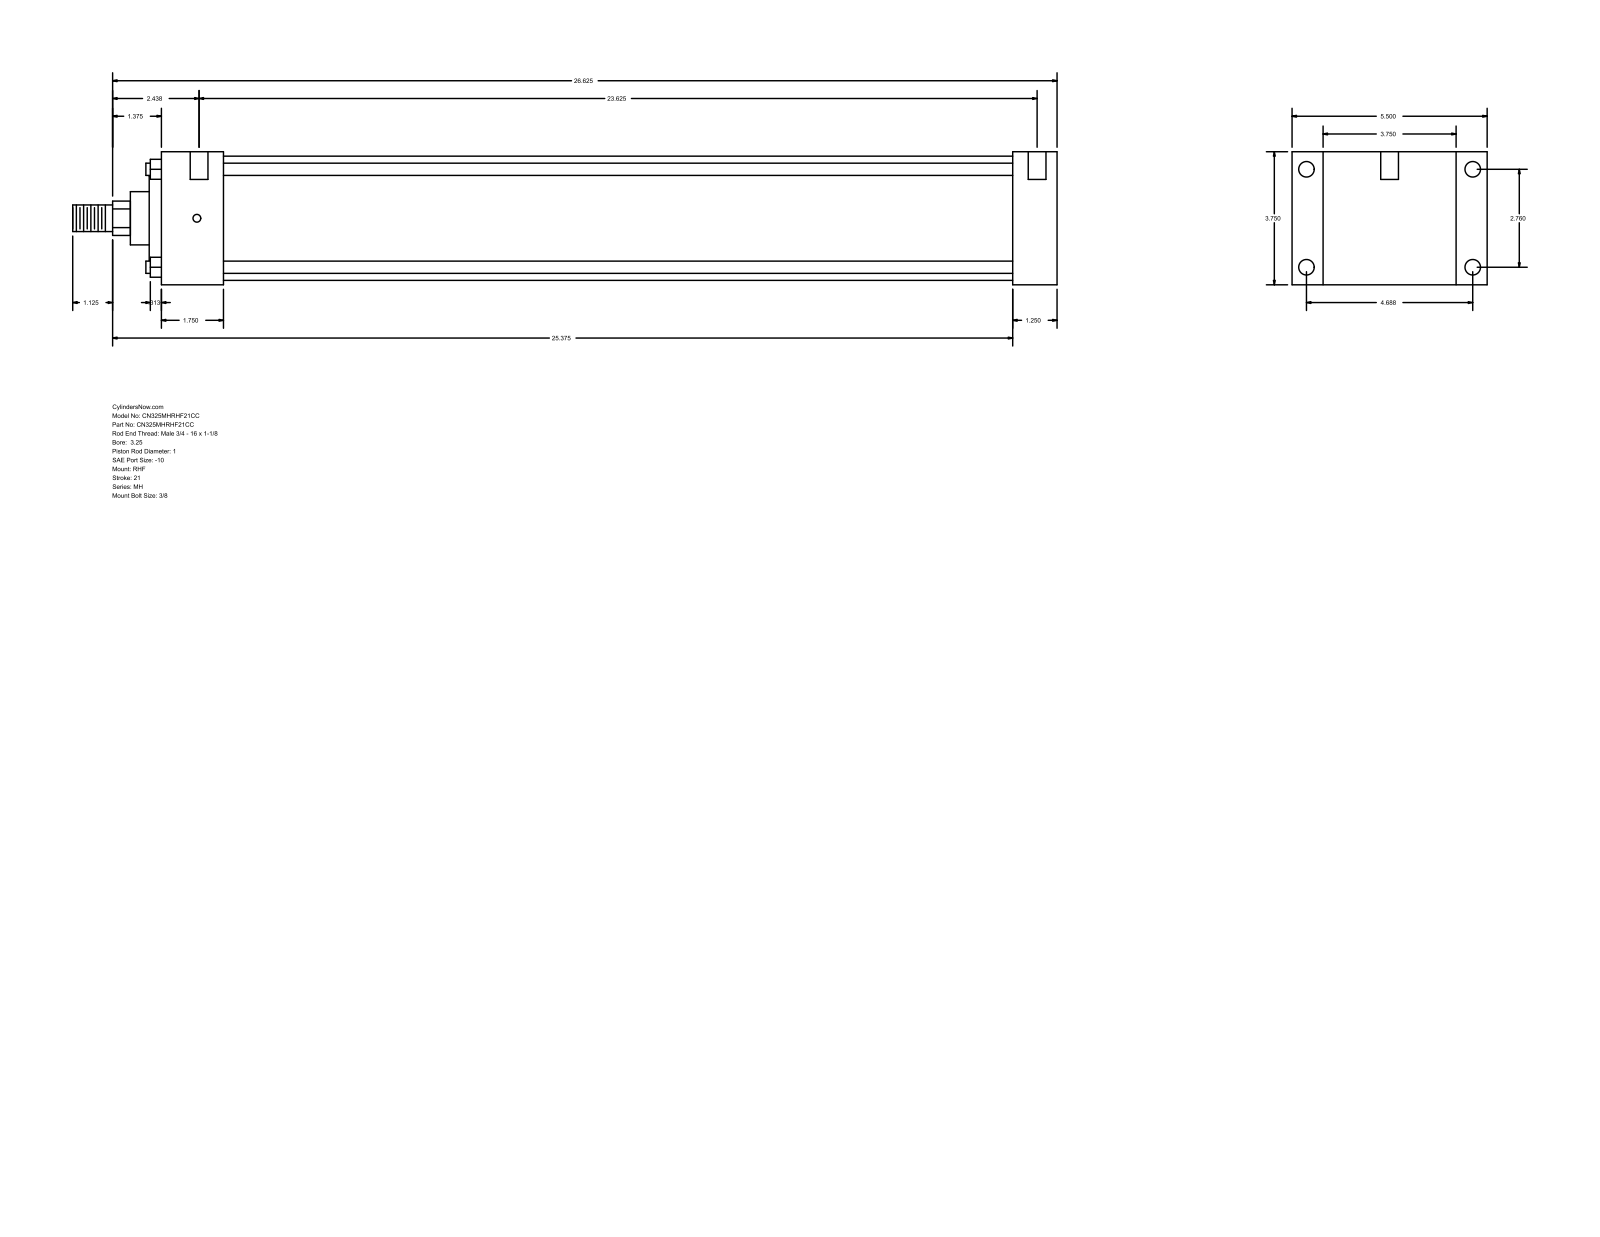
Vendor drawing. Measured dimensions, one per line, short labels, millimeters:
name: MH_RHF__0325_1
written by: GSSL Pune (CONFIG_CONTROL_DESIGN)
unit: mm
bodies: 0 solids, 90 faces (61 planar, 29 cylindrical, 0 other)
size: 704.85 × 139.7 × 95.25
holes: 4× ⌀5.56, 4× ⌀11.13, 2× ⌀12.7
bosses: 4× ⌀8.76, 1× ⌀88.9, 1× ⌀60.33, 1× ⌀38.1, 1× ⌀25.4, 1× ⌀19.05
rounds: 1× R12.29
face distances: 95.24, 31.75, 22.23, 117.47, 609.6, 641.35, 139.7, 44.46, 565.14, 596.89
hole spacings: 70.1, 119.06, 138.16, 606.42, 1.58, 4.76, 600.08, 601.66
